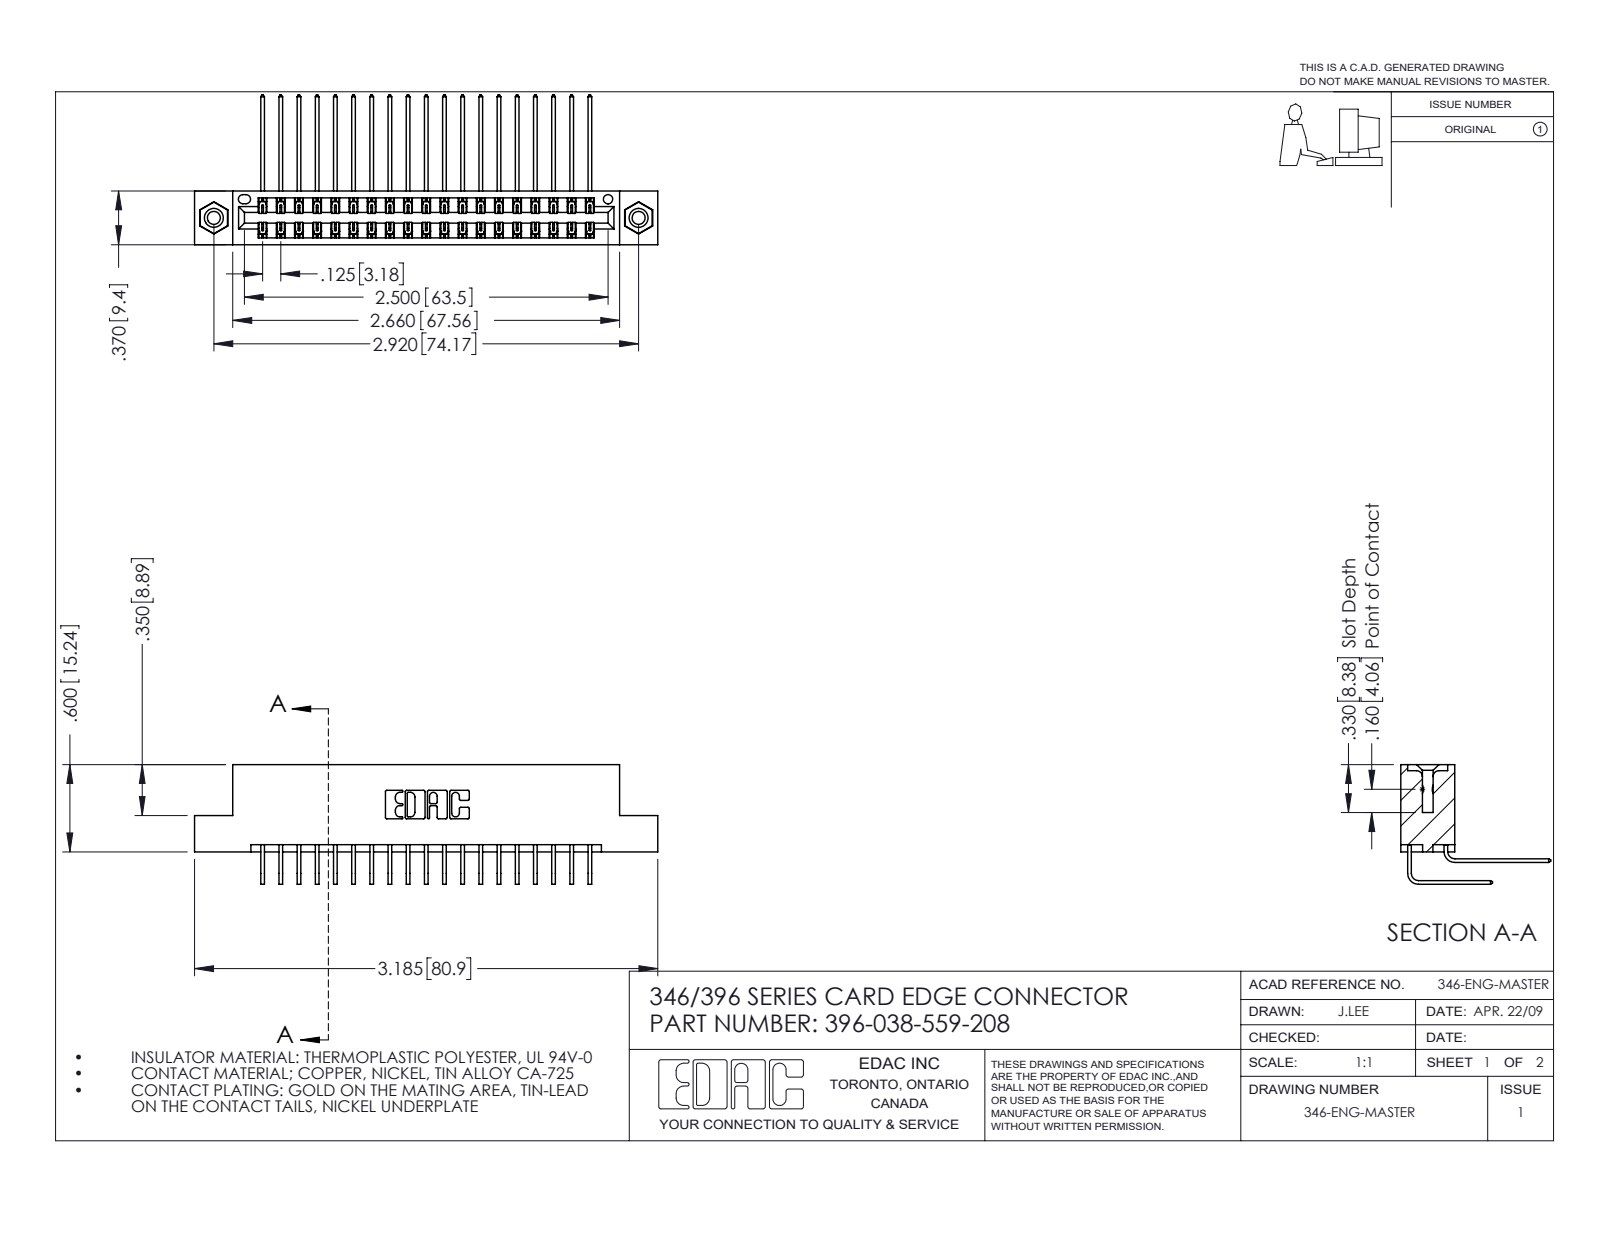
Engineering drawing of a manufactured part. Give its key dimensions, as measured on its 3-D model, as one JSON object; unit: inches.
{"part_name": "346 Part_Flush Mounting Lugs - 0.156 Dia-TI; 345-250-001_345-250-003-102; 345-292-001_558 559 Tail - 1; 396-038-559-208 (+1 more)", "step_written_by": "SolidWorks 2016 (CONFIG_CONTROL_DESIGN)", "units": "inches", "bodies": {"solids": 41, "faces": 2234, "planar": 1514, "cylindrical": 704, "other": 16}, "overall_size": [3.185, 1.03, 0.823], "volume_in3": 0.483, "surface_area_in2": 17.98, "round_holes": [[0.089, 2], [0.125, 2], [0.156, 2], [0.064, 1]], "round_bosses_or_shafts": [[0.155, 2]], "partial_cylinders_radius": [[0.006, 57], [0.01, 22], [0.007, 6], [0.031, 6], [0.026, 3], [0.014, 2], [0.022, 2], [0.024, 2]], "face_to_face_distances": [0.048, 0.322, 0.25, 0.025, 0.37, 0.072, 0.298, 0.275, 0.148, 0.222], "hole_center_spacings": [0.246, 2.713, 2.92]}
